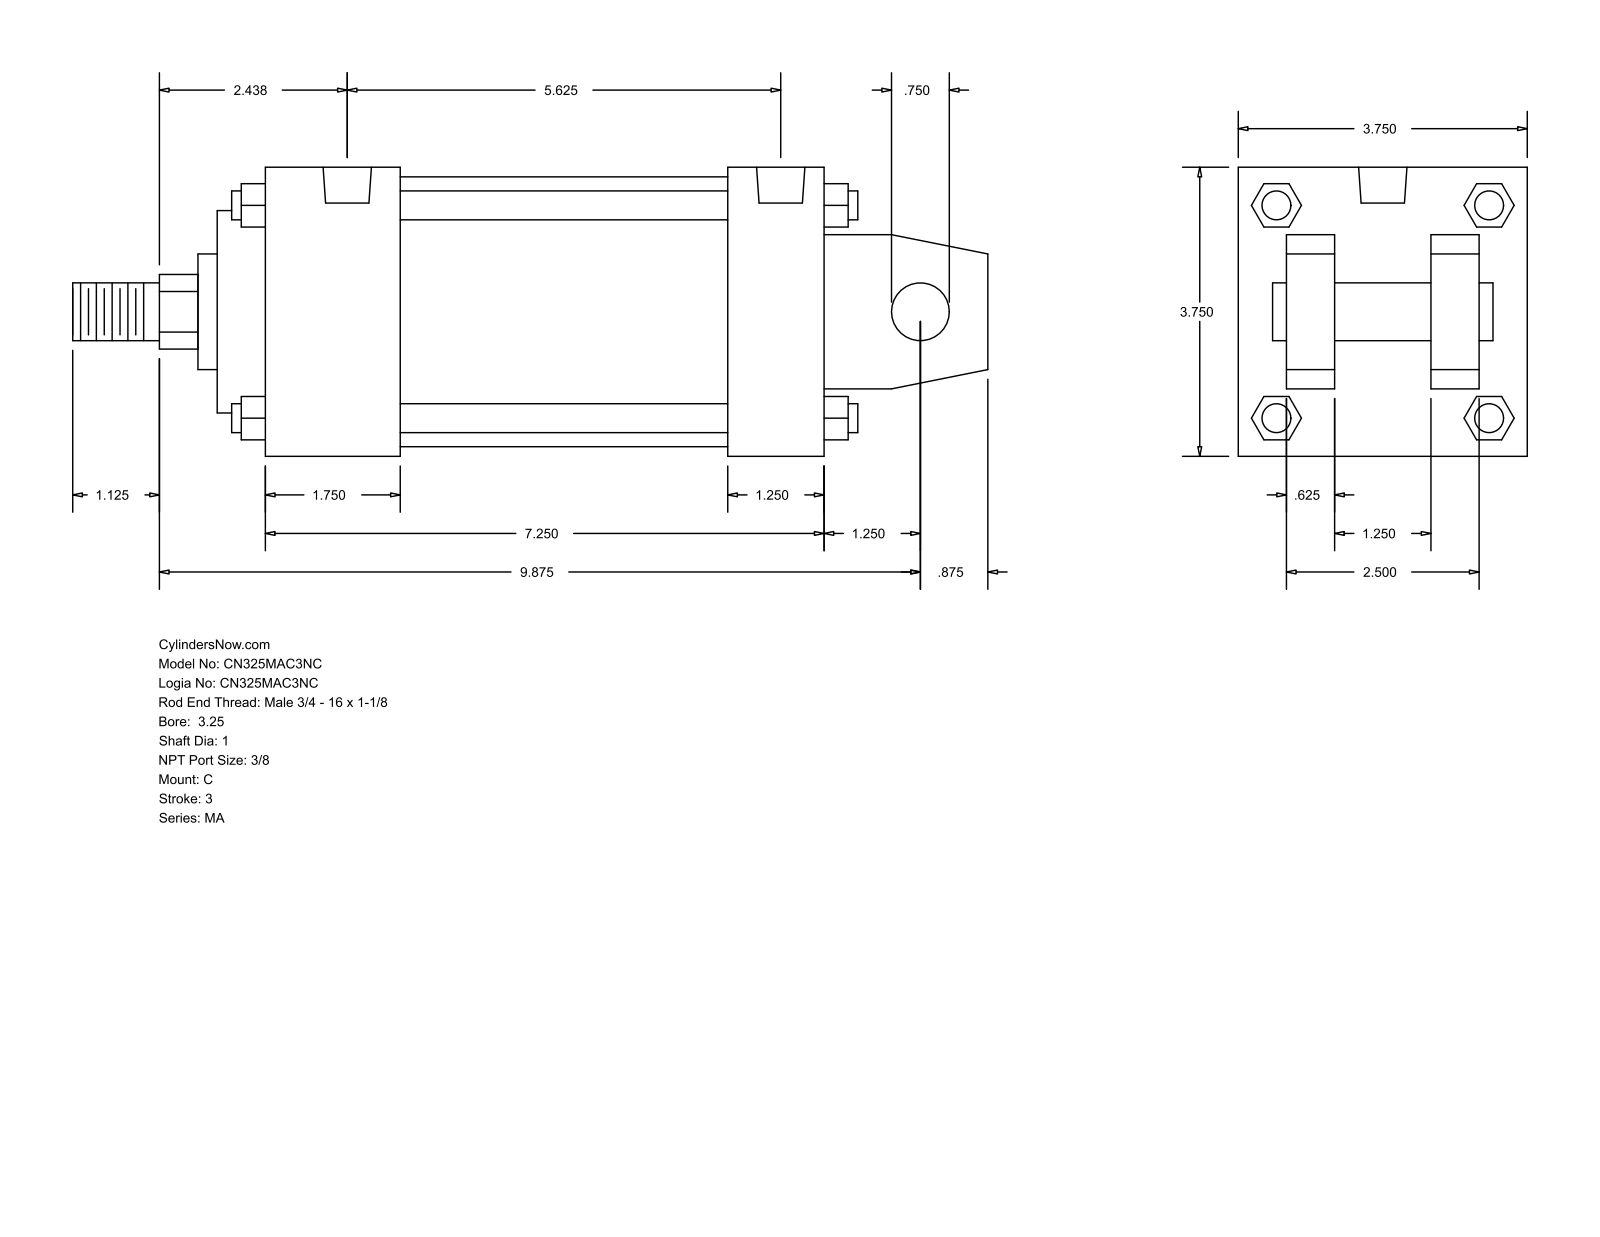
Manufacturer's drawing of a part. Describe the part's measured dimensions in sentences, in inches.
The part is named "MA_C__0325_1". Its 3-D file was written by "GSSL Pune (CONFIG_CONTROL_DESIGN)". It is 0 solids with 141 faces: 109 planar, 32 cylindrical and 0 other. Overall it measures 11.875 by 3.75 by 3.75 inches. Round holes: 4 of diameter 0.437, 2 of diameter 0.627. Round bosses or shafts: 4 of diameter 0.375, 2 of diameter 0.75, 1 of diameter 3.5, 1 of diameter 2.625, 1 of diameter 1.5, 1 of diameter 1. Partial cylindrical surfaces (rounded edges, fillets, slot ends): 1 of radius 0.484. The main face-to-face distances are 3.75, 0.625, 2.5, 7.25, 1.25, 3.125, 1.875, 7.875, 6, 1.25. The hole center spacings are 0.187, 5.25, 5.438, 5.625.
